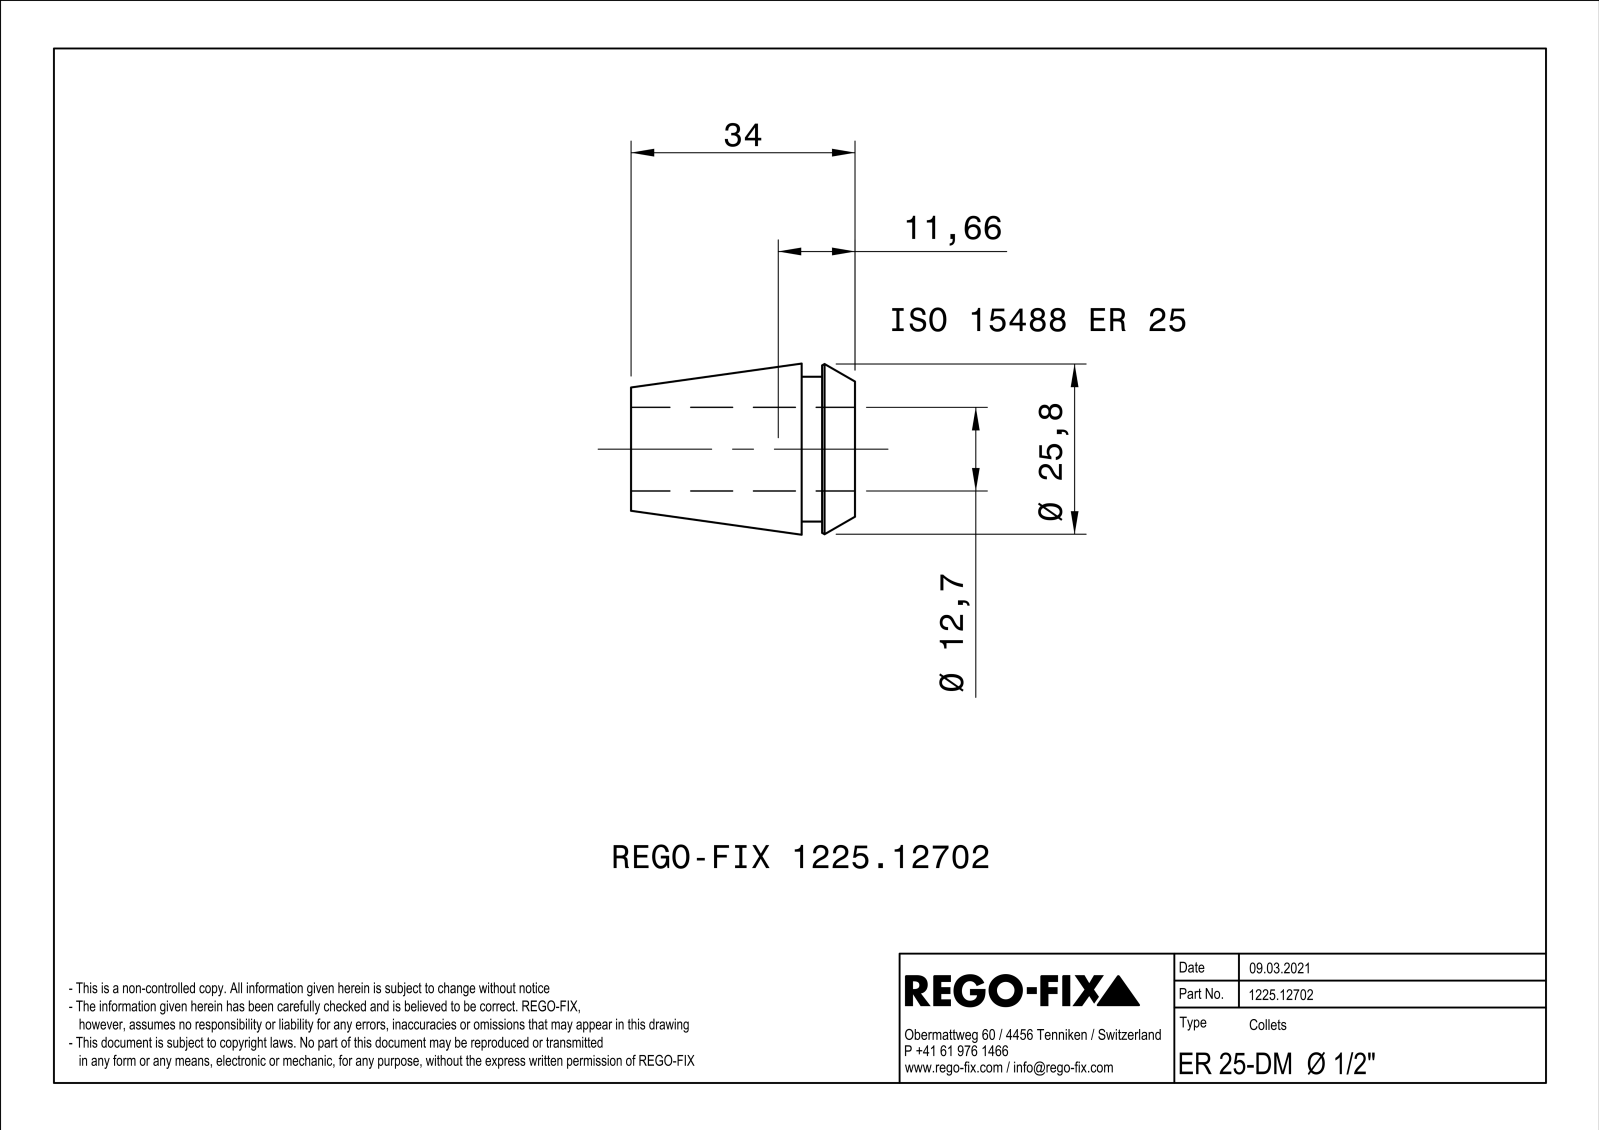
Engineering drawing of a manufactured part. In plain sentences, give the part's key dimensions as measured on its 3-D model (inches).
The part is named "NOCUT". Its 3-D file was written by "SIEMENS PLM Software Solid Edge ST10 (AUTOMOTIVE_DESIGN)". It is 1 solid with 154 faces: 80 planar, 9 cylindrical and 65 other. Overall it measures 1.339 by 1.023 by 1.023 inches. Its volume is 0.476 cubic inches and its surface area 11.67 square inches. Round holes: 1 of diameter 0.5. Round bosses or shafts: 1 of diameter 0.866. The main face-to-face distances are 0.031, 0.197, 1.142, 0.319, 1.339, 1.02, 0.122, 0.591, 0.394, 0.272.
